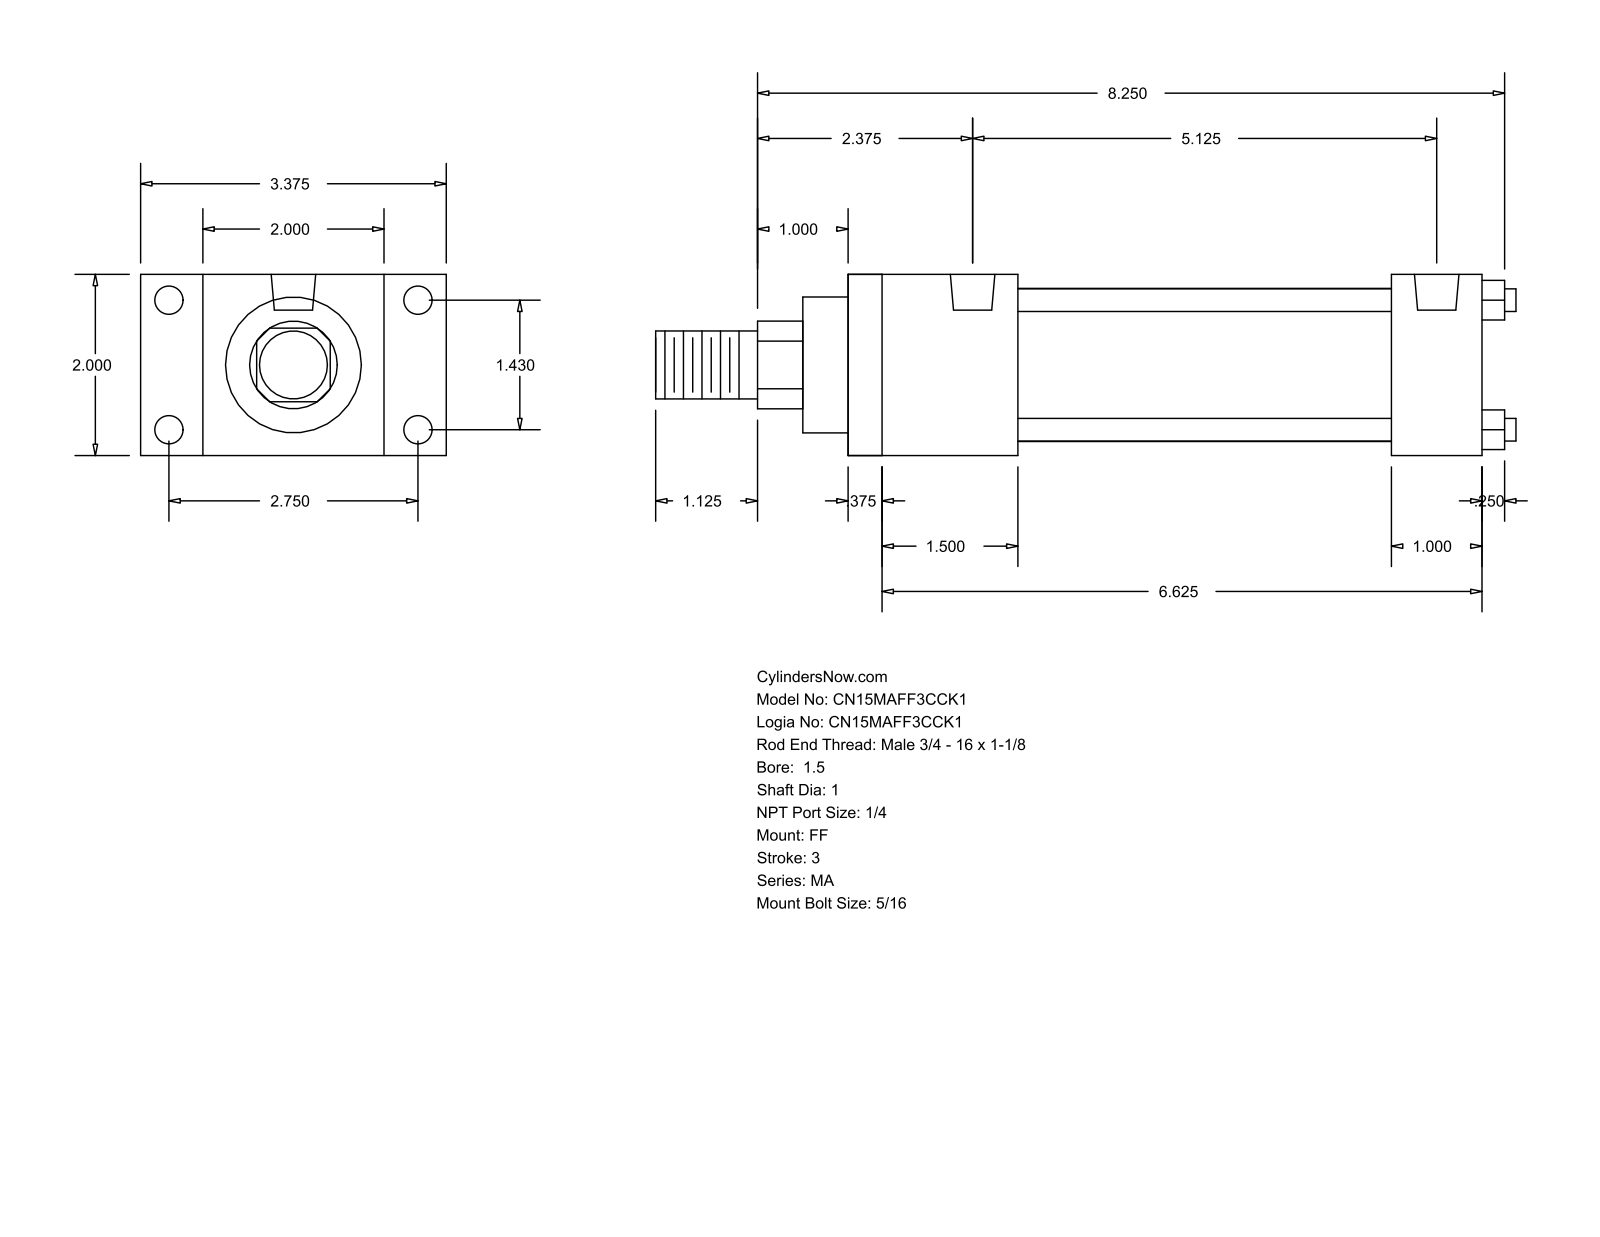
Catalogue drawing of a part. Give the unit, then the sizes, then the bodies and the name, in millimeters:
Units: millimetres
Overall size (bounding box): 241.3 × 85.72 × 50.8
Round holes (diameter × count): ⌀7.94 ×8, ⌀12.49 ×2
Round bosses / shafts (diameter × count): ⌀6.35 ×4, ⌀42.93 ×1, ⌀38.1 ×1, ⌀25.4 ×1, ⌀19.05 ×1
Partial cylindrical surfaces — rounded edges, fillets, slot ends (radius × count): R12.29 ×1
Main face-to-face distances: 50.8, 177.8, 9.52, 168.28, 25.4, 47.63, 152.4, 38.11, 142.88, 104.77
Hole centre spacings: 36.32, 69.84, 78.72, 130.17
Bodies: 0 solids, 92 faces (64 planar, 28 cylindrical, 0 other)
Part name (STEP PRODUCT): MA_FF__0150_1
STEP written by: GSSL Pune (CONFIG_CONTROL_DESIGN)
